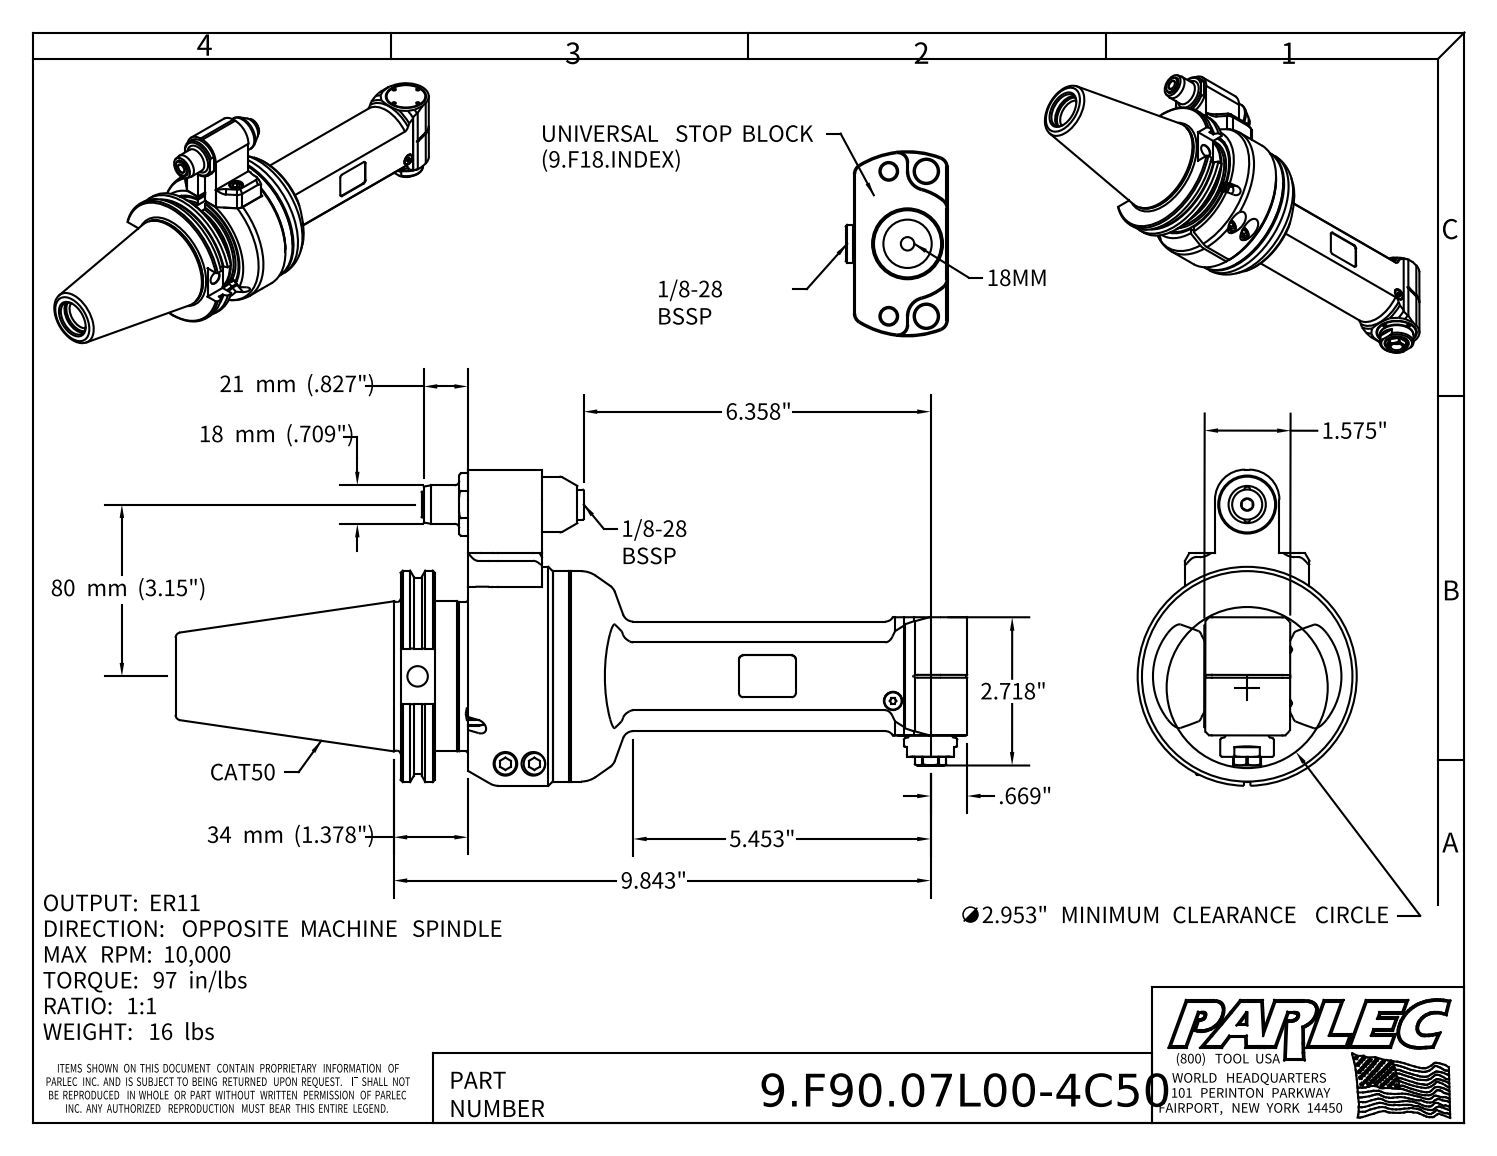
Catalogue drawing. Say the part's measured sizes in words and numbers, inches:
The part is named "9.F90.07L00-4C50; 9_GA1_458_2_4_C50; 9FL1ATC; 9F18T180_ASM (+4 more)". Its 3-D file was written by "Autodesk Inventor 2022 (AUTOMOTIVE_DESIGN)". It is 5 solids with 487 faces: 230 planar, 120 cylindrical and 137 other. Overall it measures 14.512 by 5.796 by 4.016 inches. Its volume is 77.22 cubic inches and its surface area 250.3 square inches. Round holes: 10 of diameter 0.102, 2 of diameter 0.197, 2 of diameter 0.409, 2 of diameter 0.433, 1 of diameter 0.098, 1 of diameter 0.118, 1 of diameter 0.256, 1 of diameter 0.276, 1 of diameter 0.295, 1 of diameter 0.335, 1 of diameter 0.354, 1 of diameter 0.375. Round bosses or shafts: 6 of diameter 0.236, 4 of diameter 0.394, 3 of diameter 0.709, 2 of diameter 0.315, 2 of diameter 0.098, 1 of diameter 4.016, 1 of diameter 3.875, 1 of diameter 3.858. Partial cylindrical surfaces (rounded edges, fillets, slot ends): 12 of radius 0.079, 4 of radius 0.157, 2 of radius 0.016, 2 of radius 0.02, 2 of radius 0.039, 2 of radius 0.138, 2 of radius 0.197, 2 of radius 0.551. The main face-to-face distances are 1.26, 1.575, 0.904, 2.163, 1.555, 0.625, 1.529, 2.789, 1.233, 0.608. The hole center spacings are 0.492, 0.696, 0.984, 0.696, 0.492, 0.493, 0.014, 0.276.
